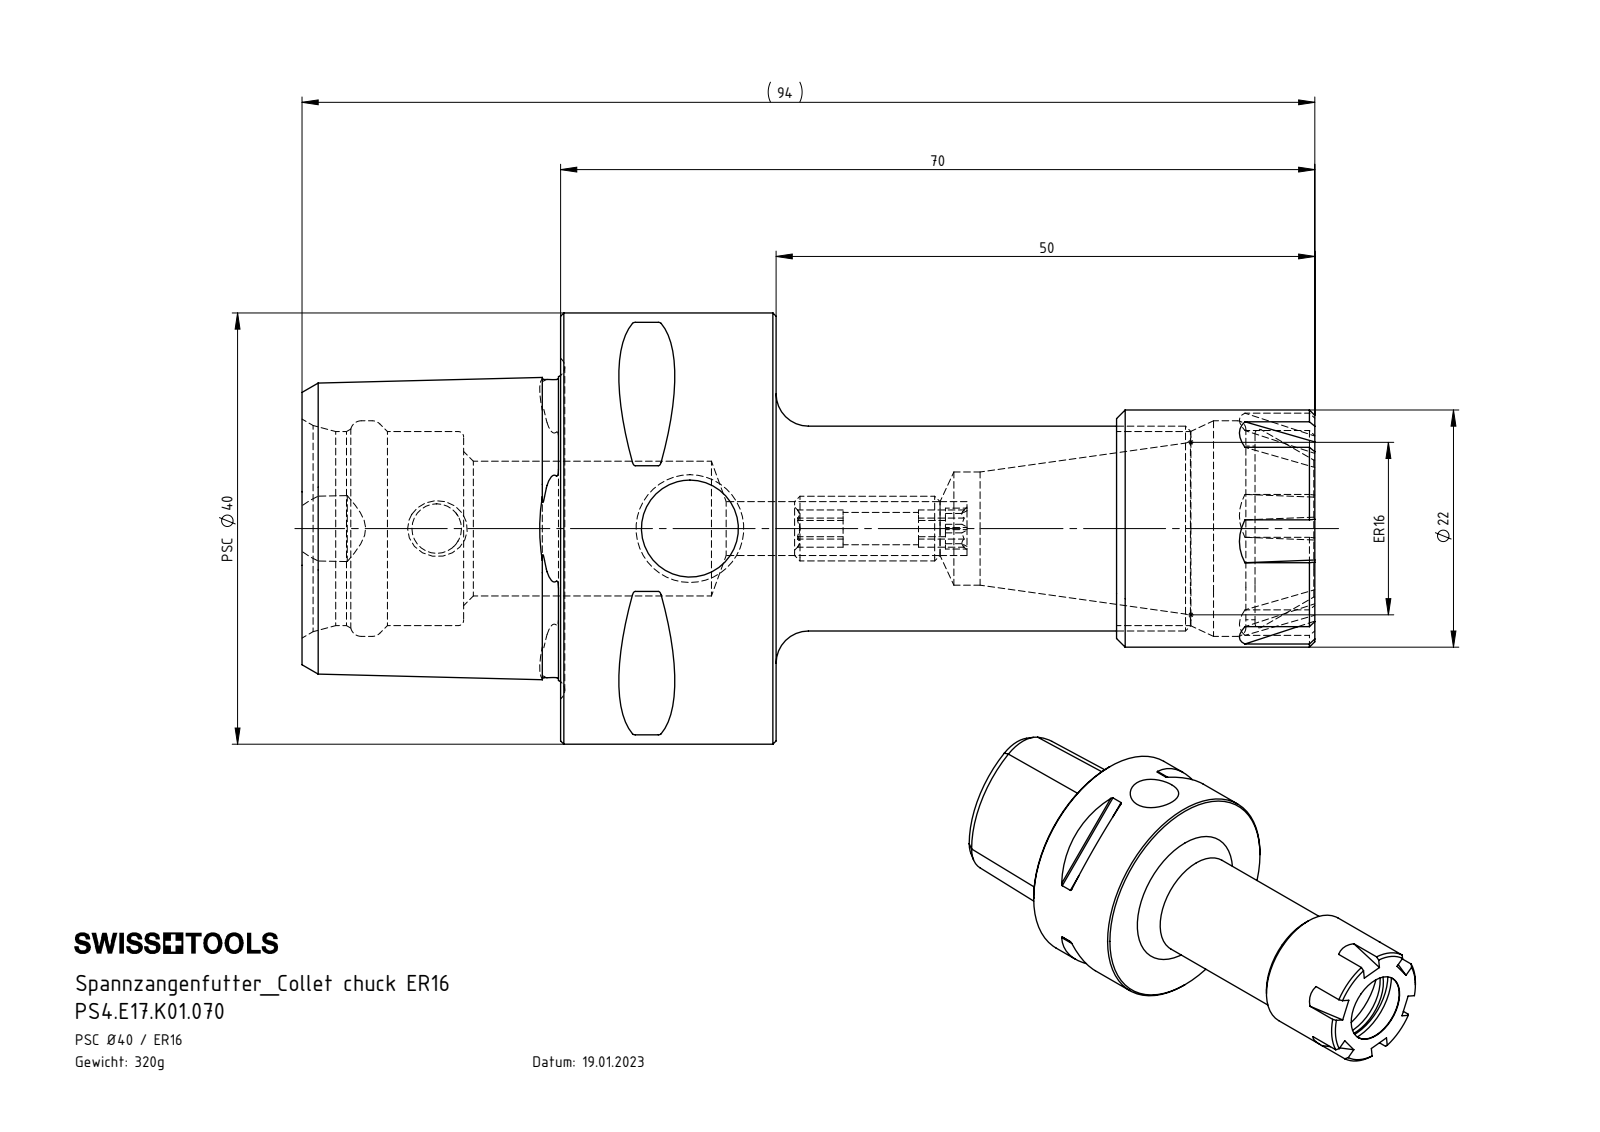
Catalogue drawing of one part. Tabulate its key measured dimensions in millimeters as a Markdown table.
| quantity | value |
| --- | --- |
| part name | E17-ER1.001.018; PS4.E17.K01.070; ERU-AN2.K01.016_A; PS4-E17.K01.070_A_Fertigbearbeitung |
| STEP written by | SolidWorks 2017 (AUTOMOTIVE_DESIGN) |
| units | millimeters |
| bodies | 3 solids, 252 faces (78 planar, 52 cylindrical, 122 other) |
| overall size | 94 × 40 × 40 |
| volume | 40 626 mm³ |
| surface area | 15 863 mm² |
| round holes (diameter × count) | 3 × 1, 4.6 × 1, 5 × 1, 9 × 1, 10 × 1, 10.5 × 1, 12.5 × 1, 12.7 × 1, 14.3 × 1, 18 × 1, 20 × 1 |
| round bosses / shafts (diameter × count) | 40 × 1, 22 × 1, 19 × 1, 6 × 1 |
| partial cylindrical surfaces (radius × count) | 0.3 × 8, 7.7 × 2, 4 × 1 |
| main face-to-face distances | 20, 70, 50, 24, 44, 94, 15.52, 35.3, 75.6, 51.6 |
| hole center spacings | 23.5 |
